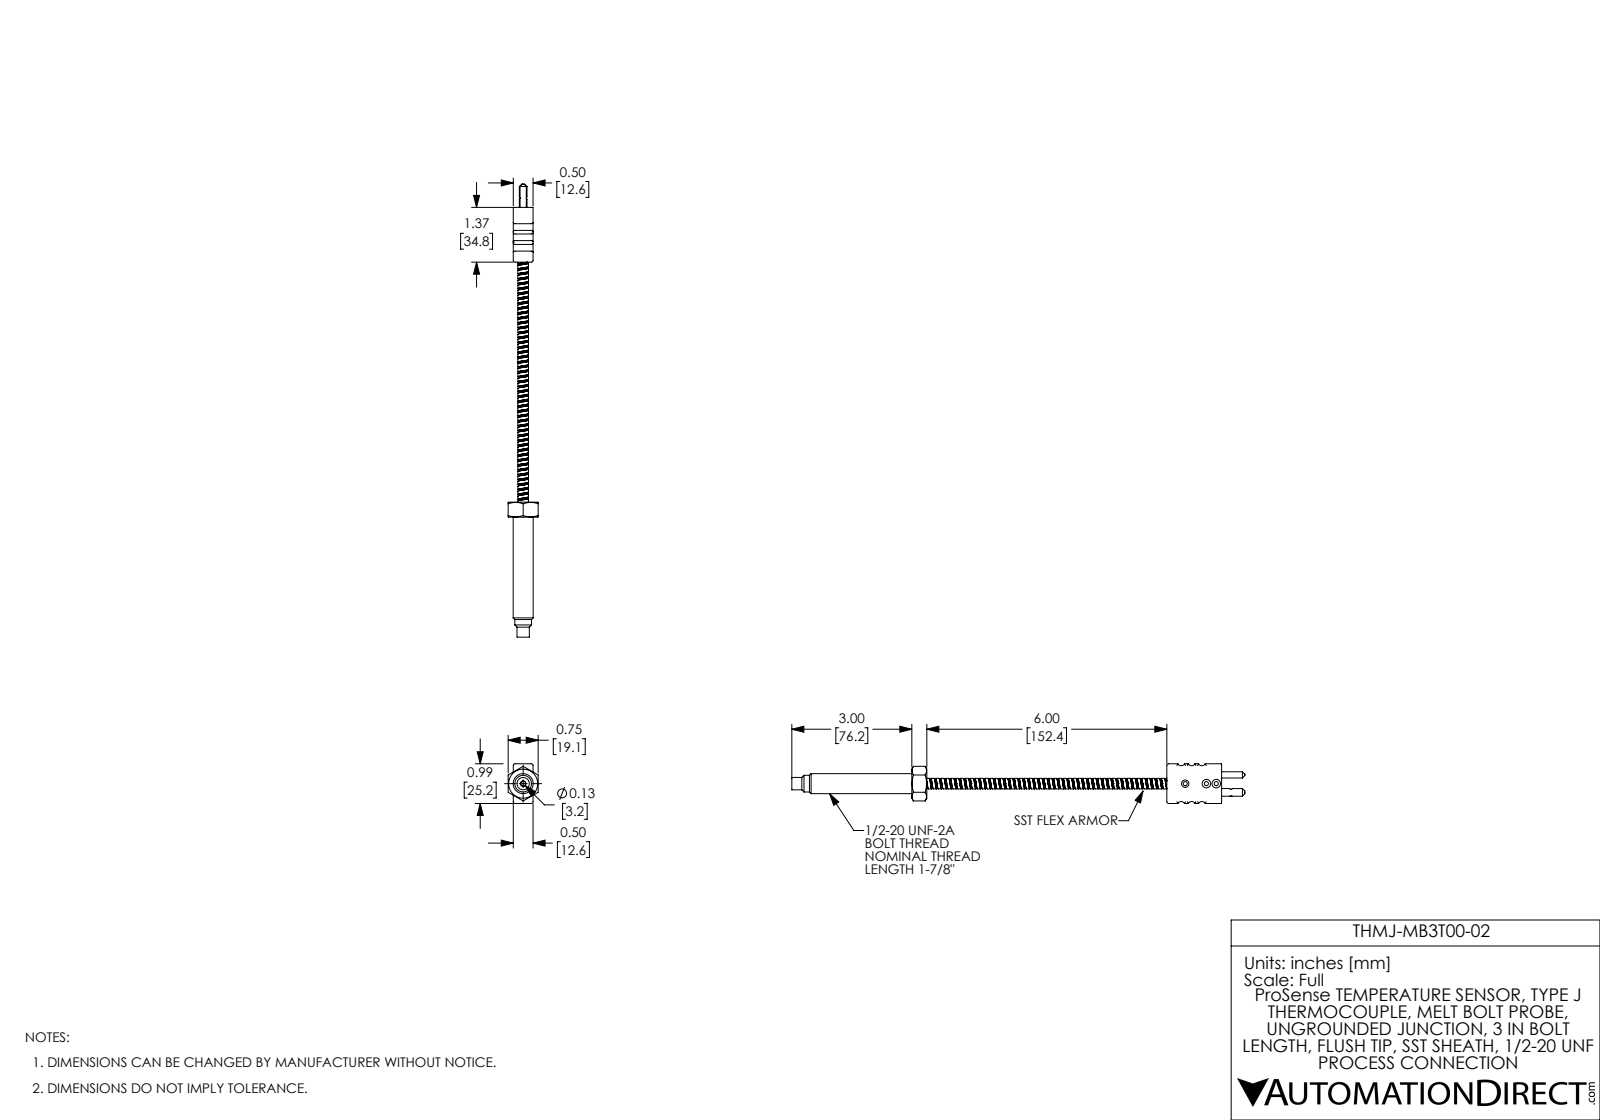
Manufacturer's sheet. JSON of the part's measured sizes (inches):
{"part_name": "THMJ-MB3T00-02", "step_written_by": "SolidWorks 2017 (AUTOMOTIVE_DESIGN)", "units": "inches", "bodies": {"solids": 3, "faces": 312, "planar": 69, "cylindrical": 172, "other": 71}, "overall_size": [11.326, 0.993, 0.75], "volume_in3": 1.682, "surface_area_in2": 19.11, "round_holes": [[0.103, 2], [0.158, 2], [0.135, 1], [0.185, 1], [0.294, 1], [0.308, 1]], "round_bosses_or_shafts": [[0.5, 1], [0.417, 1], [0.309, 1], [0.278, 1], [0.265, 1], [0.191, 1], [0.156, 1], [0.125, 1]], "partial_cylinders_radius": [[0.045, 8], [0.095, 6], [0.01, 4]], "face_to_face_distances": [0.495, 0.75, 7.369, 0.993, 0.127, 0.622, 1.369, 6, 7.744, 6.375], "hole_center_spacings": [0.217, 0.328, 0.572, 0.247, 0.433, 0.529, 0.776]}
